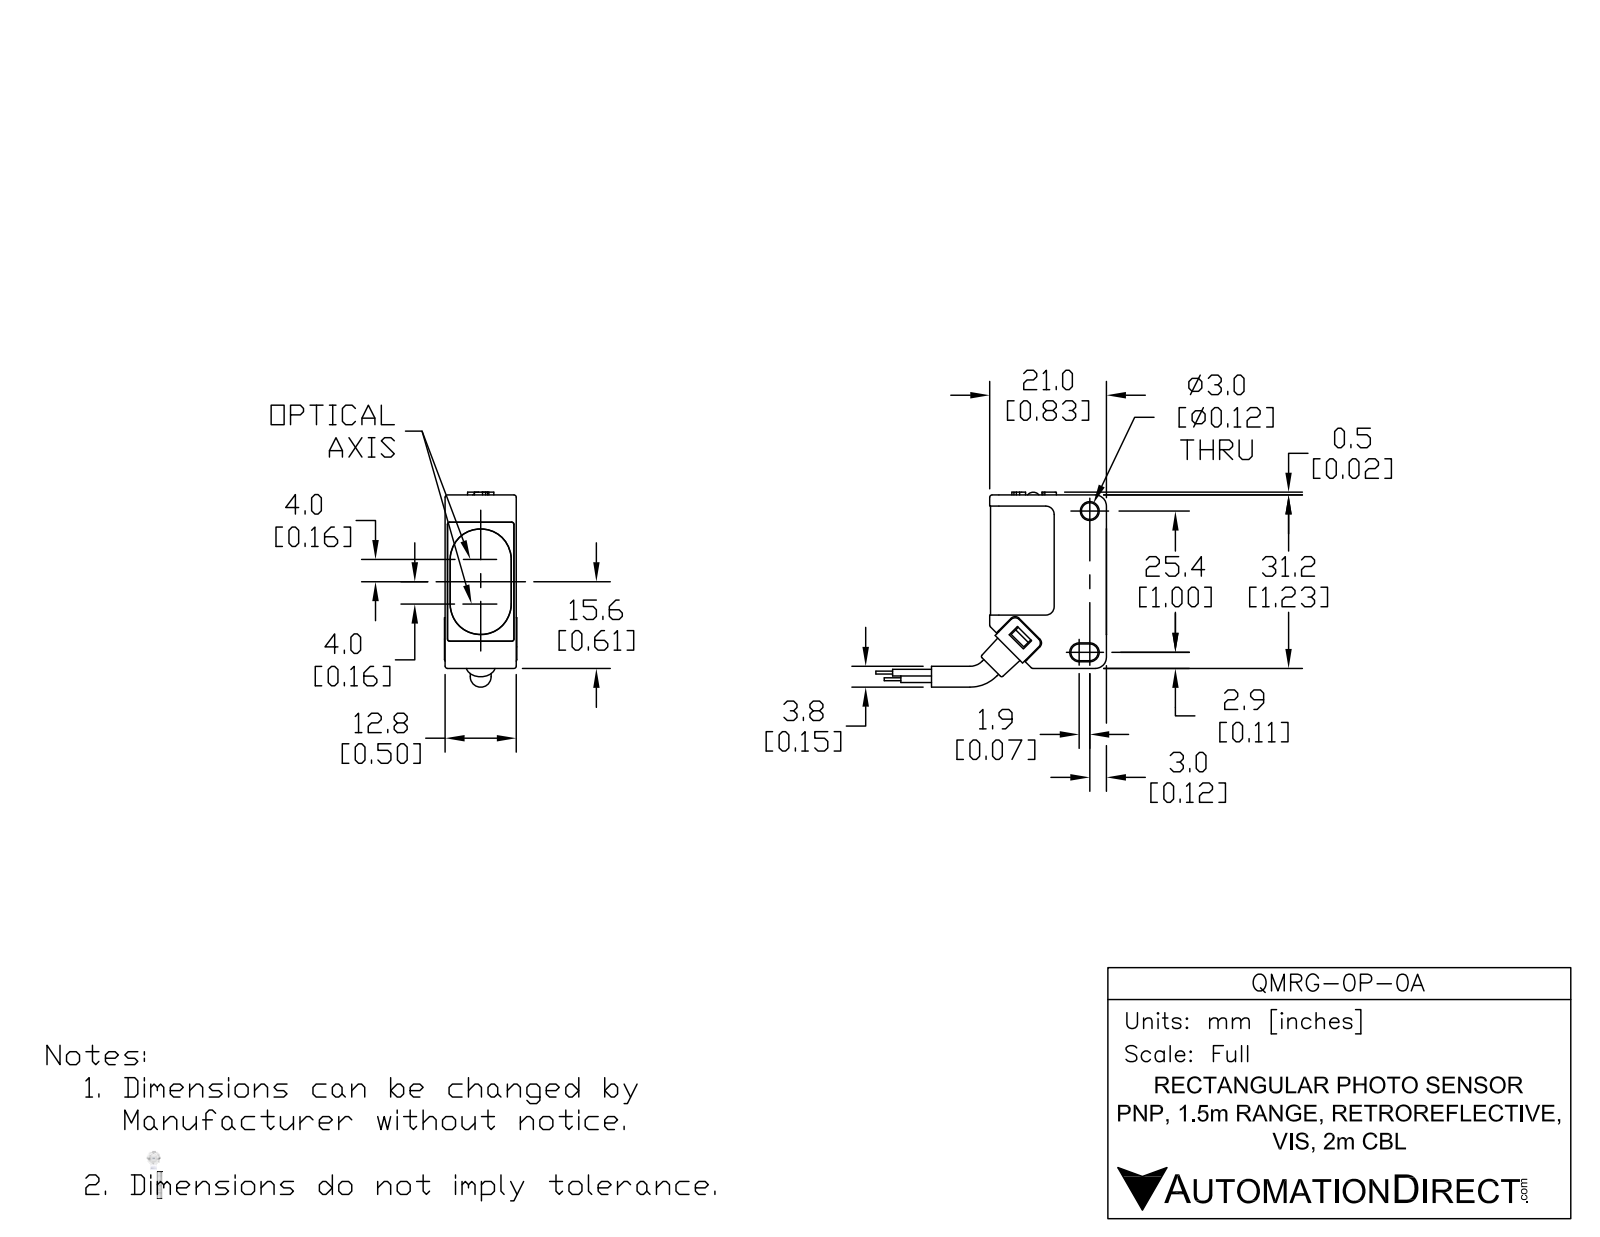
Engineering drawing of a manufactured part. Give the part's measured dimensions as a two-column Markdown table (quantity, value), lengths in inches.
| quantity | value |
| --- | --- |
| part name | QMRG-0P-0A |
| STEP written by | SolidWorks 2017 (AUTOMOTIVE_DESIGN) |
| units | inches |
| bodies | 9 solids, 258 faces (134 planar, 100 cylindrical, 24 other) |
| overall size | 3.193 × 1.032 × 0.512 |
| volume | 0.47 in³ |
| surface area | 8.375 in² |
| round holes (diameter × count) | 0.118 × 3, 0.148 × 1, 0.224 × 1, 0.283 × 1 |
| round bosses / shafts (diameter × count) | 0.138 × 2 |
| partial cylindrical surfaces (radius × count) | 0.016 × 13, 0.02 × 10, 0.039 × 8, 0.059 × 6, 0.024 × 4, 0.006 × 2, 0.035 × 2, 0.044 × 2 |
| main face-to-face distances | 0.02, 0.498, 0.059, 0.016, 0.504, 0.138, 0.488, 0.079, 0.482, 0.492 |
| hole center spacings | 0.205 |
